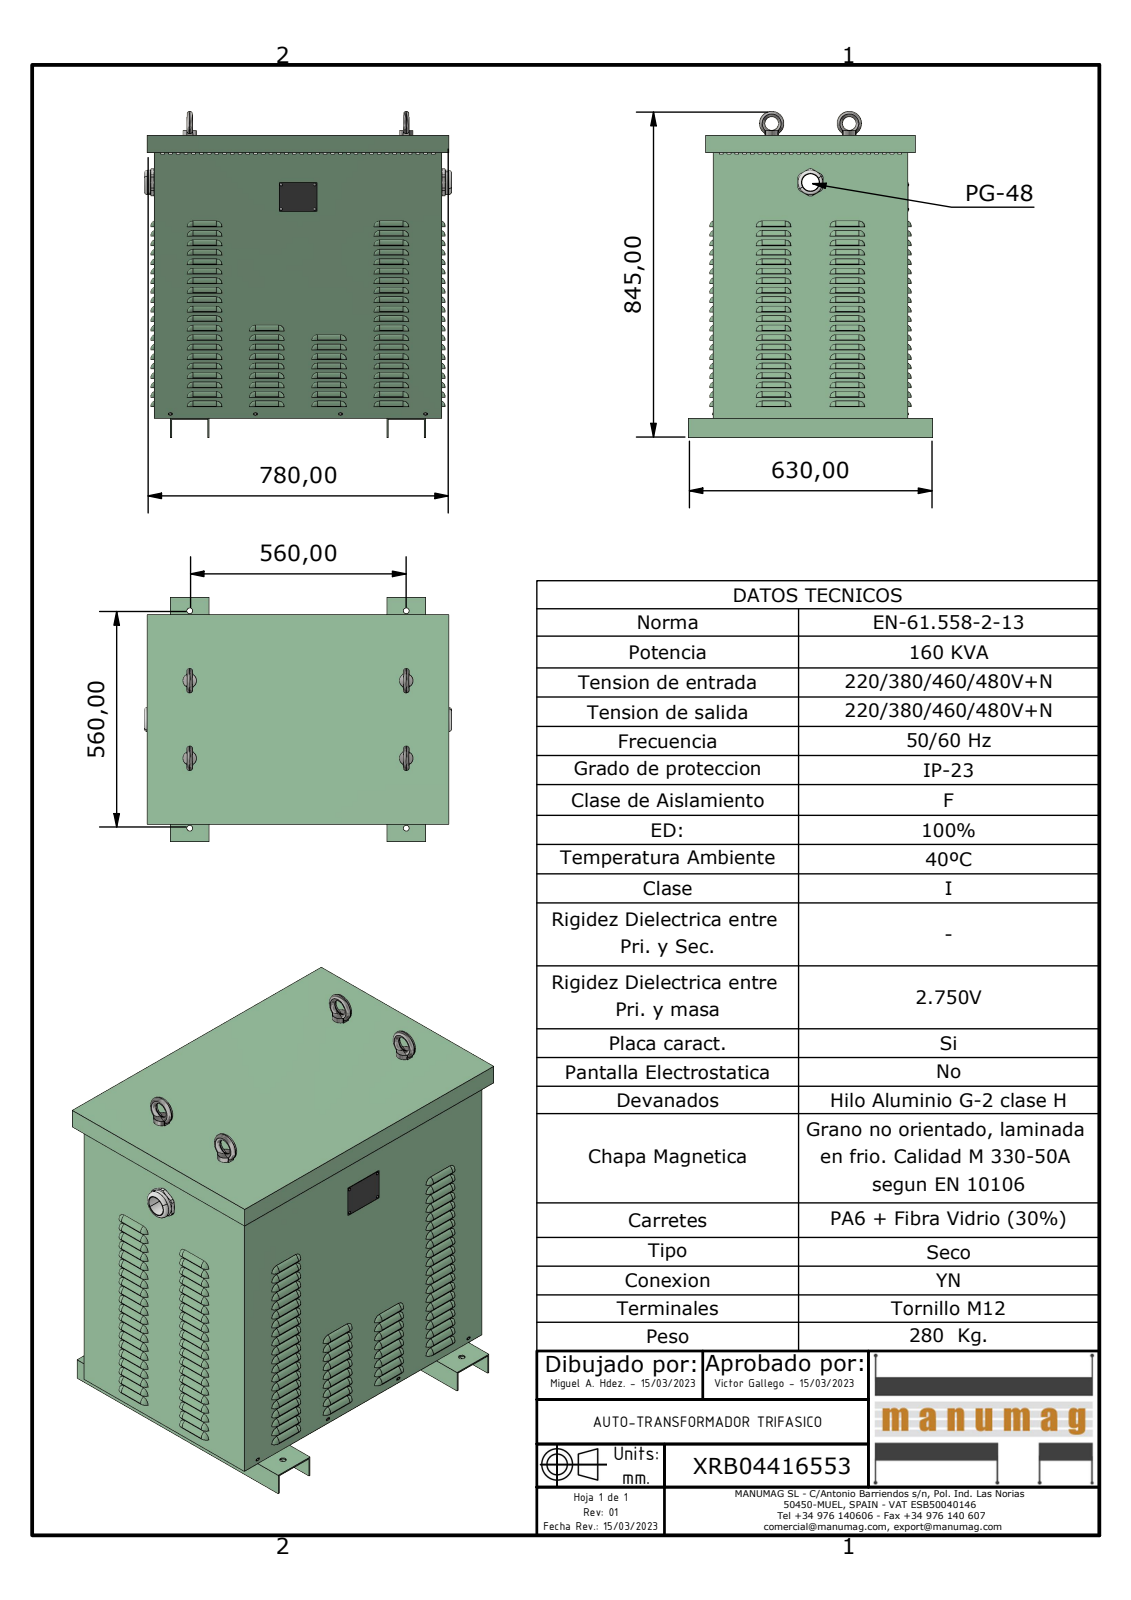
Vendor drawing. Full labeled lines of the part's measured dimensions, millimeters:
Part name (STEP PRODUCT): XRB04416553; JE160 EXPORT JE200 EXPORT NACIONAL BASE; JE160 EXPORT JE200 EXPORT NACIONAL PATA; JE160 EXPORT CUERPO (+5 more)
STEP written by: Autodesk Inventor 2023 (AUTOMOTIVE_DESIGN)
Units: millimetres
Bodies: 24 solids, 4187 faces (1441 planar, 1866 cylindrical, 880 other)
Overall size (bounding box): 844 × 795.27 × 630
Volume: 7 086 000 mm³ · Surface area: 6 256 000 mm²
Round holes (diameter × count): ⌀11 ×936, ⌀15 ×8, ⌀4 ×4, ⌀5 ×4, ⌀35 ×2, ⌀44 ×1, ⌀60 ×1
Round bosses / shafts (diameter × count): ⌀3.2 ×8, ⌀16 ×4, ⌀14.8 ×4, ⌀63 ×3, ⌀59.3 ×1, ⌀59.15 ×1, ⌀57.63 ×1
Partial cylindrical surfaces — rounded edges, fillets, slot ends (radius × count): R14 ×194, R7 ×84, R15 ×80, R2.5 ×8, R2 ×4, R17.5 ×4, R35 ×1
Main face-to-face distances: 2, 500, 730, 742, 498, 502, 732, 740, 728, 744
Hole centre spacings: 15, 30, 33.54, 204.55, 159.71, 204, 129.87, 159
